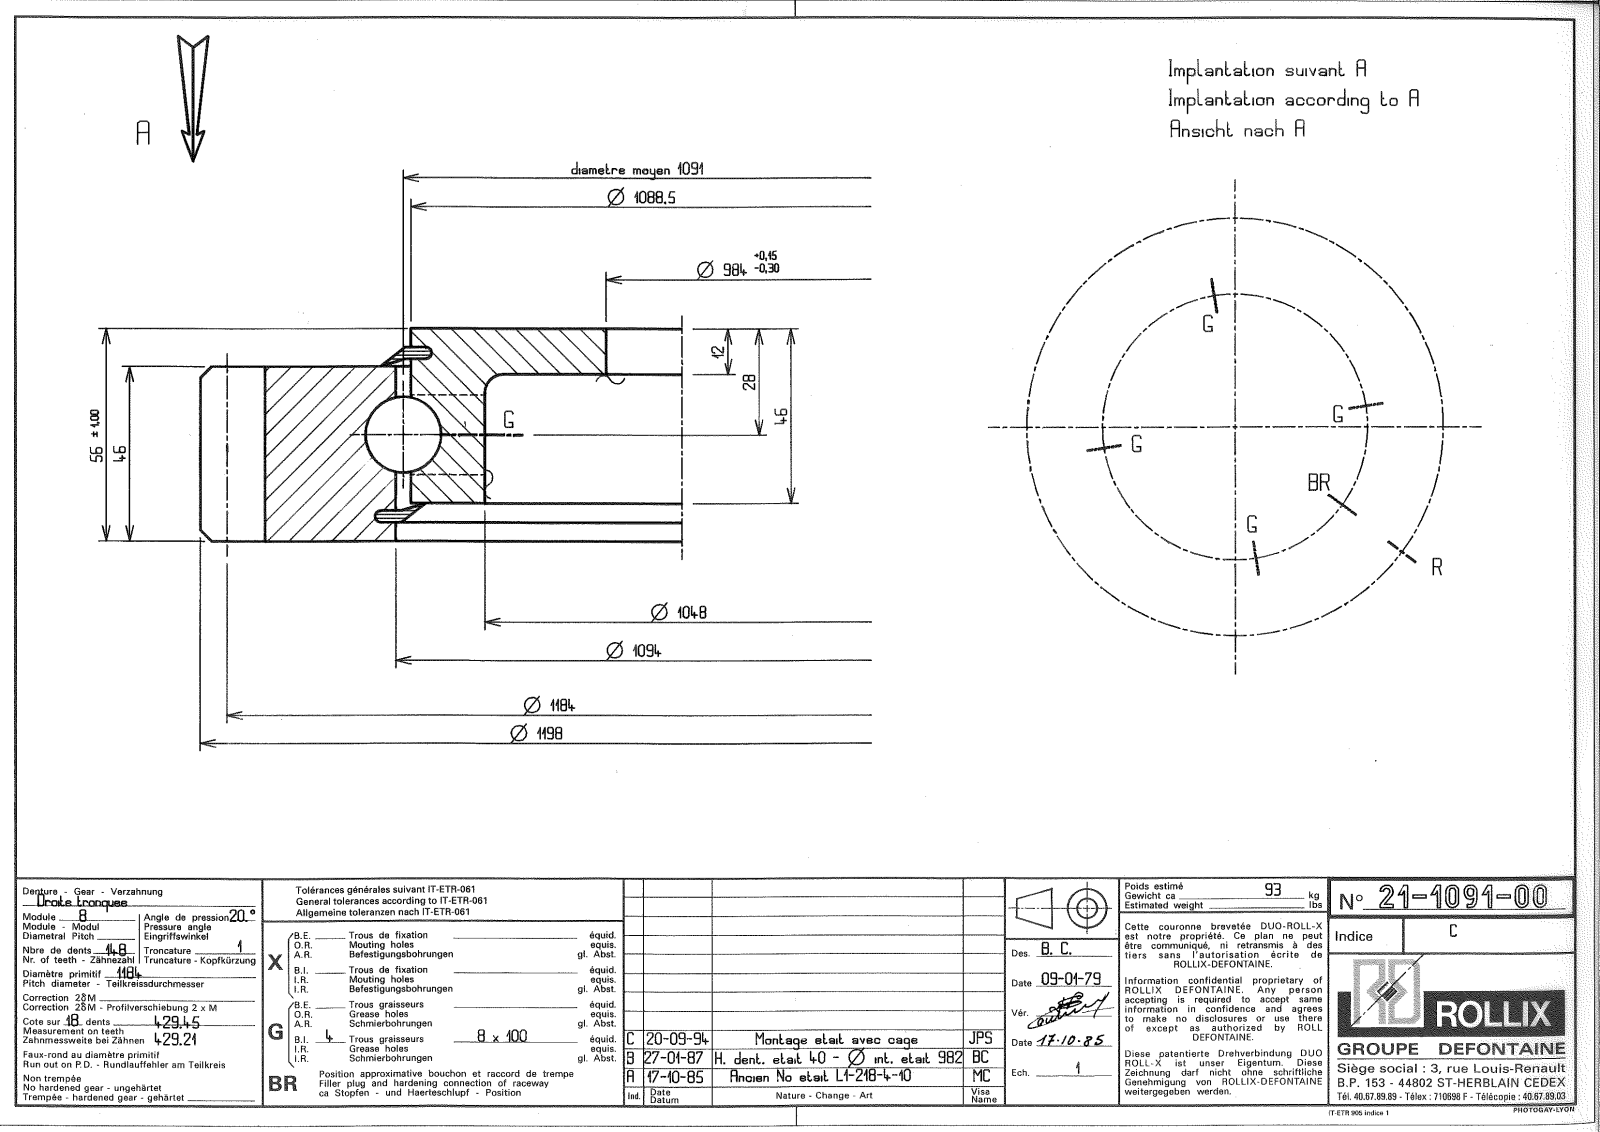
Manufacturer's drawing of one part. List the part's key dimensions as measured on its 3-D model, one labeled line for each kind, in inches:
Part name (STEP PRODUCT): 21-1091-00
STEP written by: SolidWorks 2016 (CONFIG_CONTROL_DESIGN)
Units: inches
Bodies: 9 solids, 1044 faces (349 planar, 329 cylindrical, 366 other)
Overall size (bounding box): 47.16 × 47.16 × 2.205
Volume: 656 in³ · Surface area: 2 708 in²
Round holes (diameter × count): ⌀0.276 ×4, ⌀38.74 ×1, ⌀41.26 ×1, ⌀43.13 ×1
Round bosses / shafts (diameter × count): ⌀0.315 ×4, ⌀42.776 ×1
Partial cylindrical surfaces — rounded edges, fillets, slot ends (radius × count): R22.913 ×1, R23.583 ×1
Main face-to-face distances: 0.394, 1.811, 2.205, 1.732, 0.079, 0.472, 1.339, 1.417, 0.317, 1.888
Hole centre spacings: 0.013
